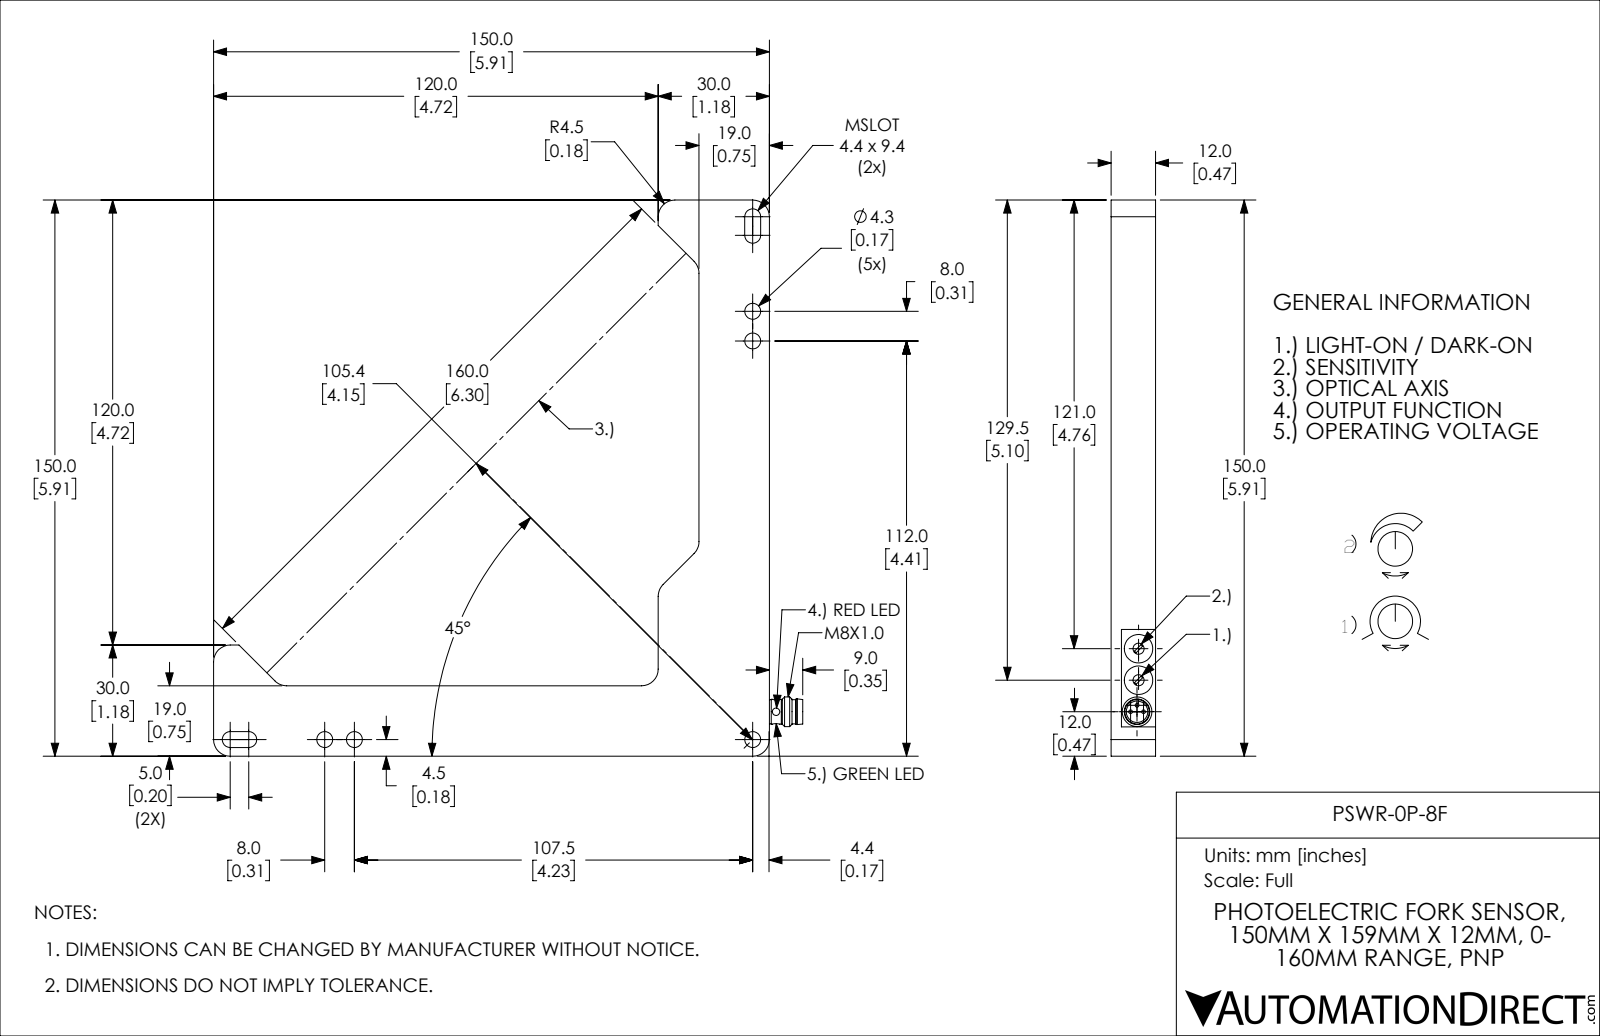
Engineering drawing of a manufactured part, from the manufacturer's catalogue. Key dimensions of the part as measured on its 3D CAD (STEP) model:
Part name (STEP PRODUCT): PSWR-0P-8F
STEP written by: SolidWorks 2017 (AUTOMOTIVE_DESIGN)
Units: inches
Bodies: 1 solid, 90 faces (42 planar, 41 cylindrical, 7 other)
Overall size (bounding box): 6.26 × 5.906 × 0.472
Volume: 4.256 in³ · Surface area: 32.08 in²
Round holes (diameter × count): ⌀0.169 ×5, ⌀0.079 ×2, ⌀0.118 ×2, ⌀0.303 ×2, ⌀0.228 ×1
Round bosses / shafts (diameter × count): ⌀0.039 ×3, ⌀0.315 ×1, ⌀0.272 ×1, ⌀0.264 ×1, ⌀0.257 ×1
Partial cylindrical surfaces — rounded edges, fillets, slot ends (radius × count): R0.177 ×10, R0.085 ×4, R0.049 ×2
Main face-to-face distances: 0.472, 0.748, 5.906, 5.157, 1.181, 0.433, 4.724, 6.298, 0.093, 0.262
Hole centre spacings: 0.315, 4.232, 4.547, 6.212, 0.335, 0.335, 0.385, 0.669
